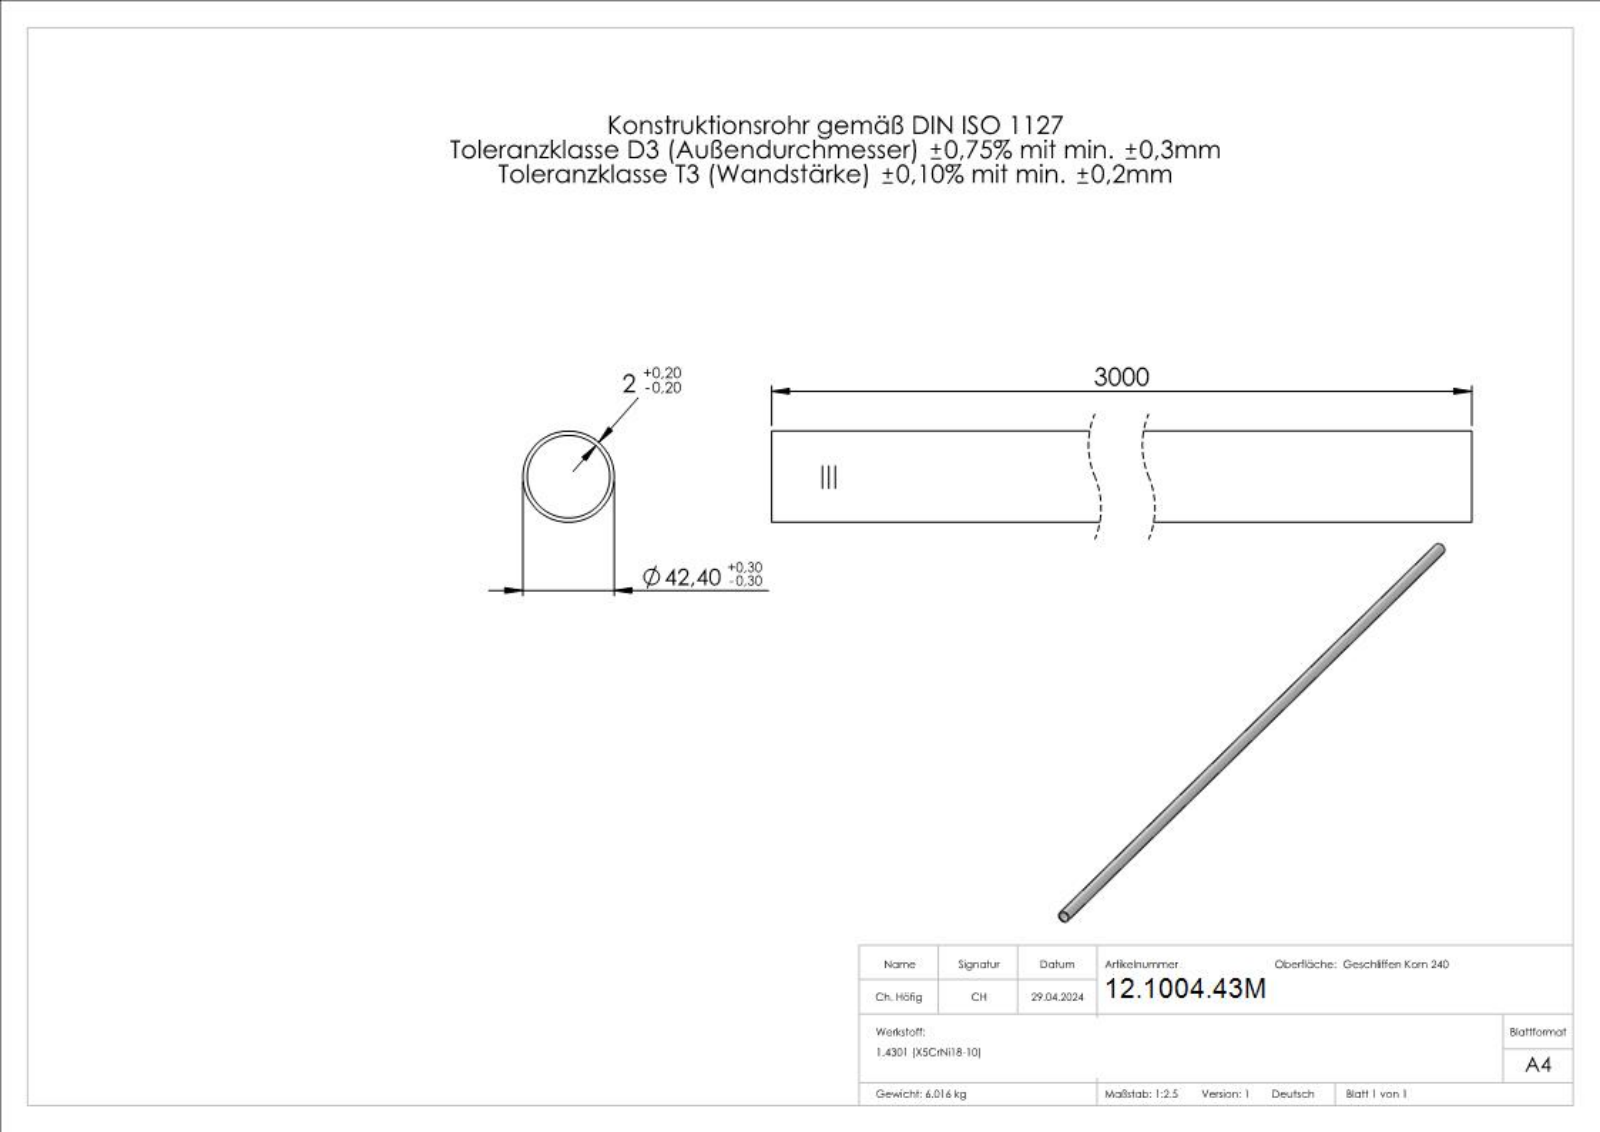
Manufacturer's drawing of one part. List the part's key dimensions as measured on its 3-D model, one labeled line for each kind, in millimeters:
Part name (STEP PRODUCT): 55130-2403M
STEP written by: SolidWorks 2018 (CONFIG_CONTROL_DESIGN)
Units: millimetres
Bodies: 1 solid, 302 faces (138 planar, 28 cylindrical, 136 other)
Overall size (bounding box): 3000 × 42.4 × 42.4
Volume: 761 522 mm³ · Surface area: 762 038 mm²
Round holes (diameter × count): ⌀38.4 ×1
Round bosses / shafts (diameter × count): ⌀42.4 ×1
Partial cylindrical surfaces — rounded edges, fillets, slot ends (radius × count): R19.3 ×1
Main face-to-face distances: 3000, 1.57, 1.78, 2.41, 0.73, 2.61, 0.79, 0.65, 2.24, 2.45
